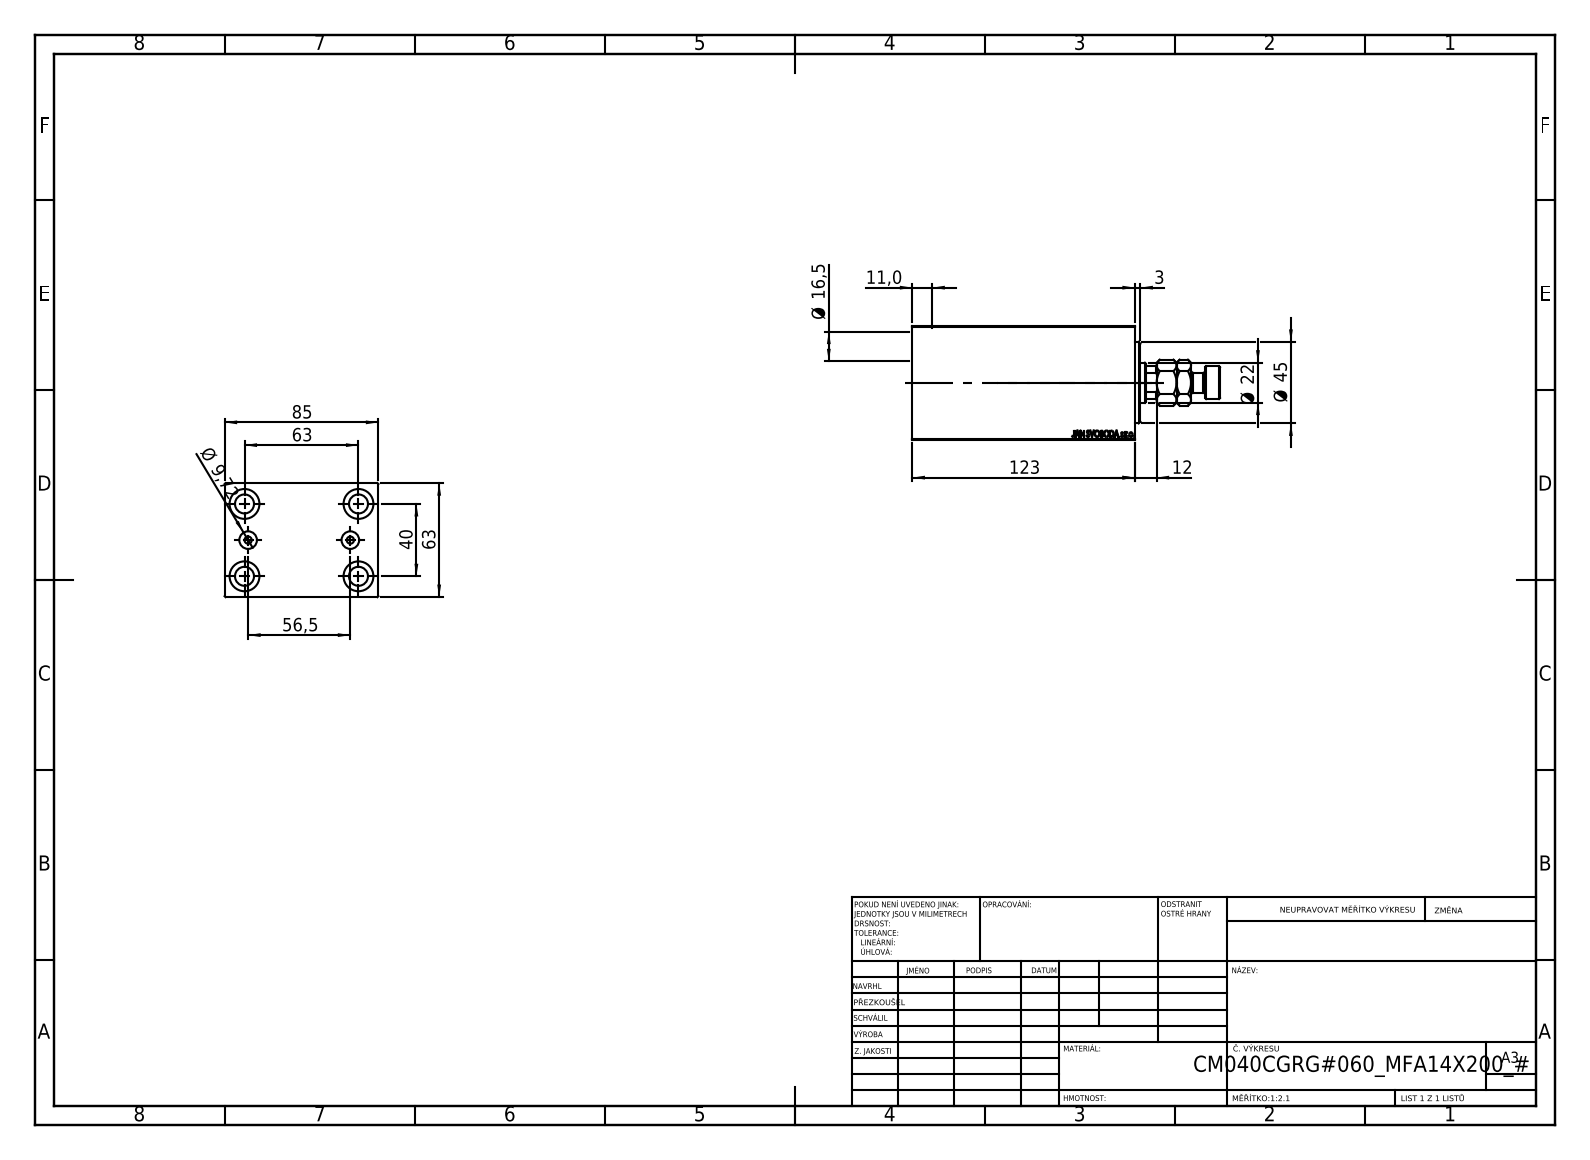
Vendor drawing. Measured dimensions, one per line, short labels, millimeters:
name: V450CM_C_Body; V450CM_VC_B; MFA; V450CM_C_VCP
written by: SolidWorks 2019 (CONFIG_CONTROL_DESIGN)
unit: mm
bodies: 4 solids, 910 faces (424 planar, 60 cylindrical, 426 other)
size: 170 × 85 × 63
volume: 563 575 mm³; area: 104 232 mm²
holes: 4× ⌀10.5, 4× ⌀16.5, 2× ⌀4, 2× ⌀9.72, 1× ⌀12.5, 1× ⌀22, 1× ⌀25.5, 1× ⌀40, 1× ⌀42, 1× ⌀45
bosses: 1× ⌀18, 1× ⌀11
rounds: 1× R10.5
face distances: 63, 85, 12, 111, 123, 1, 99, 11, 112, 100
hole spacings: 37.31, 20.1, 20.5, 40, 61.82, 63, 64.2, 74.63
